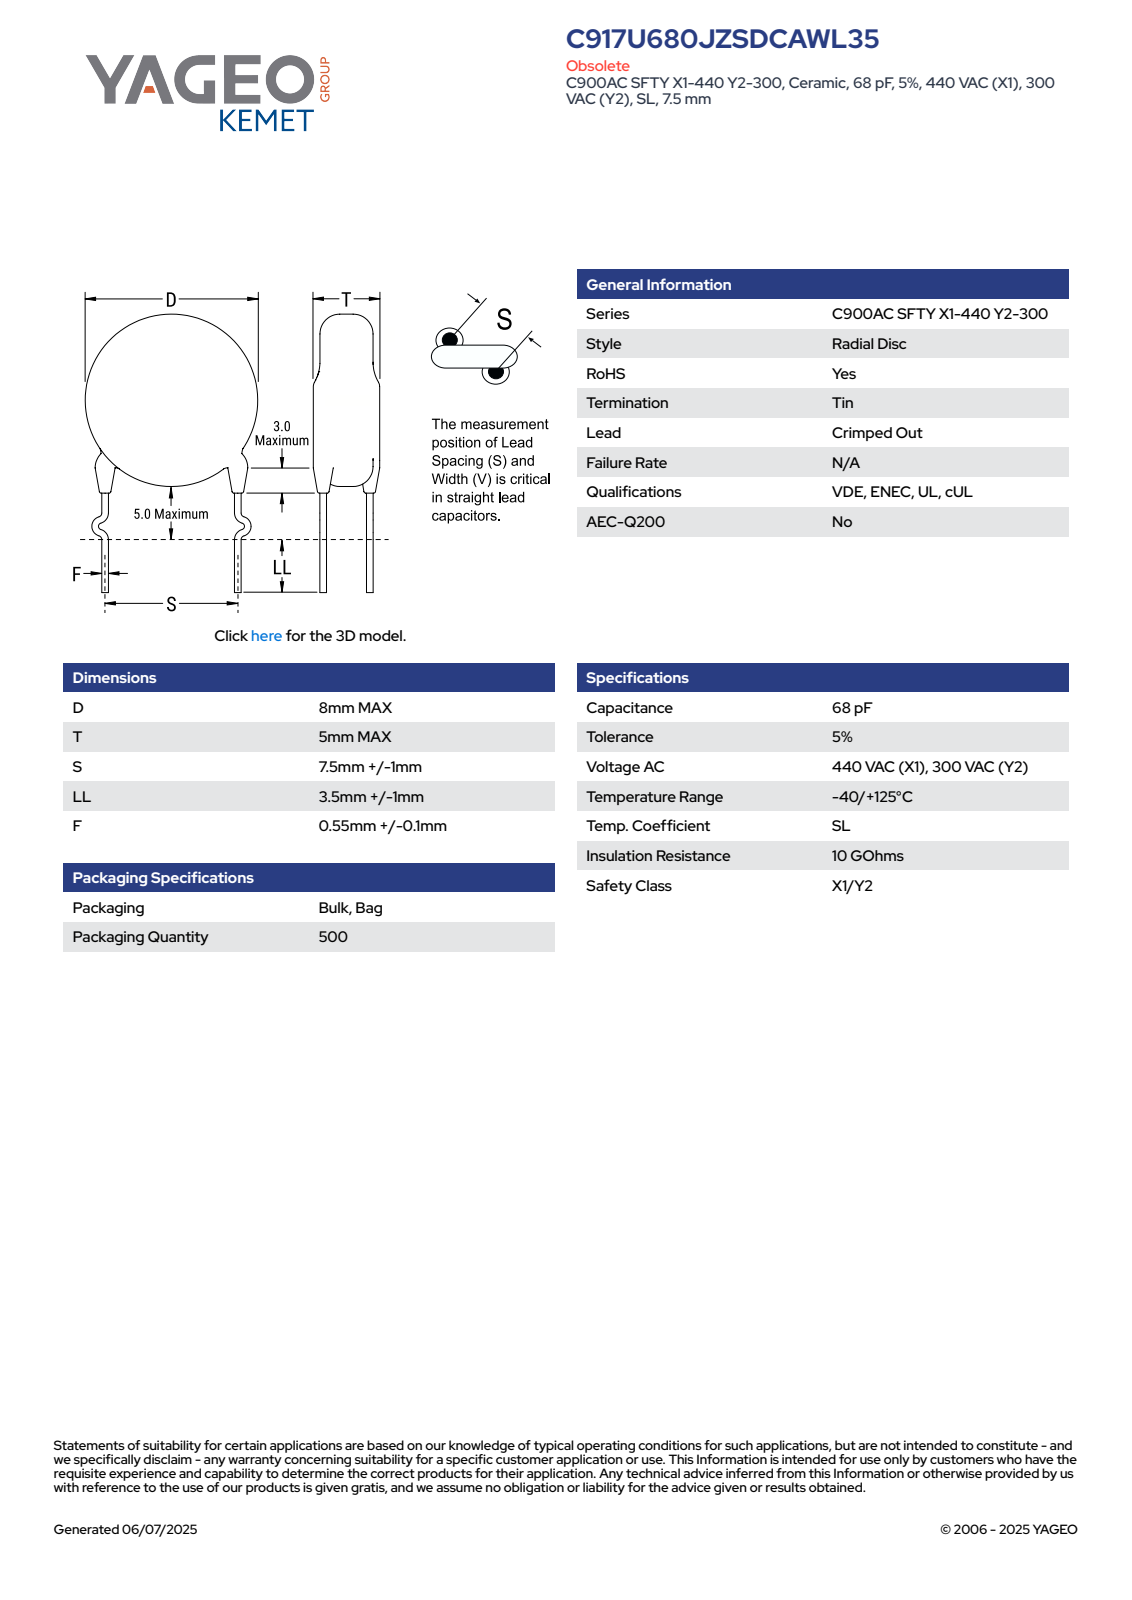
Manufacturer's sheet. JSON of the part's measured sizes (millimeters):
{"part_name": "CCD_KCOC900_D8T5S7.5LL4.5F0.55", "step_written_by": "SolidWorks 2014 (AUTOMOTIVE_DESIGN)", "units": "millimeters", "bodies": {"solids": 4, "faces": 87, "planar": 63, "cylindrical": 6, "other": 18}, "overall_size": [17.5, 12.09, 5.04], "volume_mm3": 253, "surface_area_mm2": 271, "round_bosses_or_shafts": [[1.2, 2], [8, 1]], "face_to_face_distances": [5, 0.83, 4.42, 3.59, 3.39, 0.52, 0.31, 0.67, 1.71, 2.46]}
